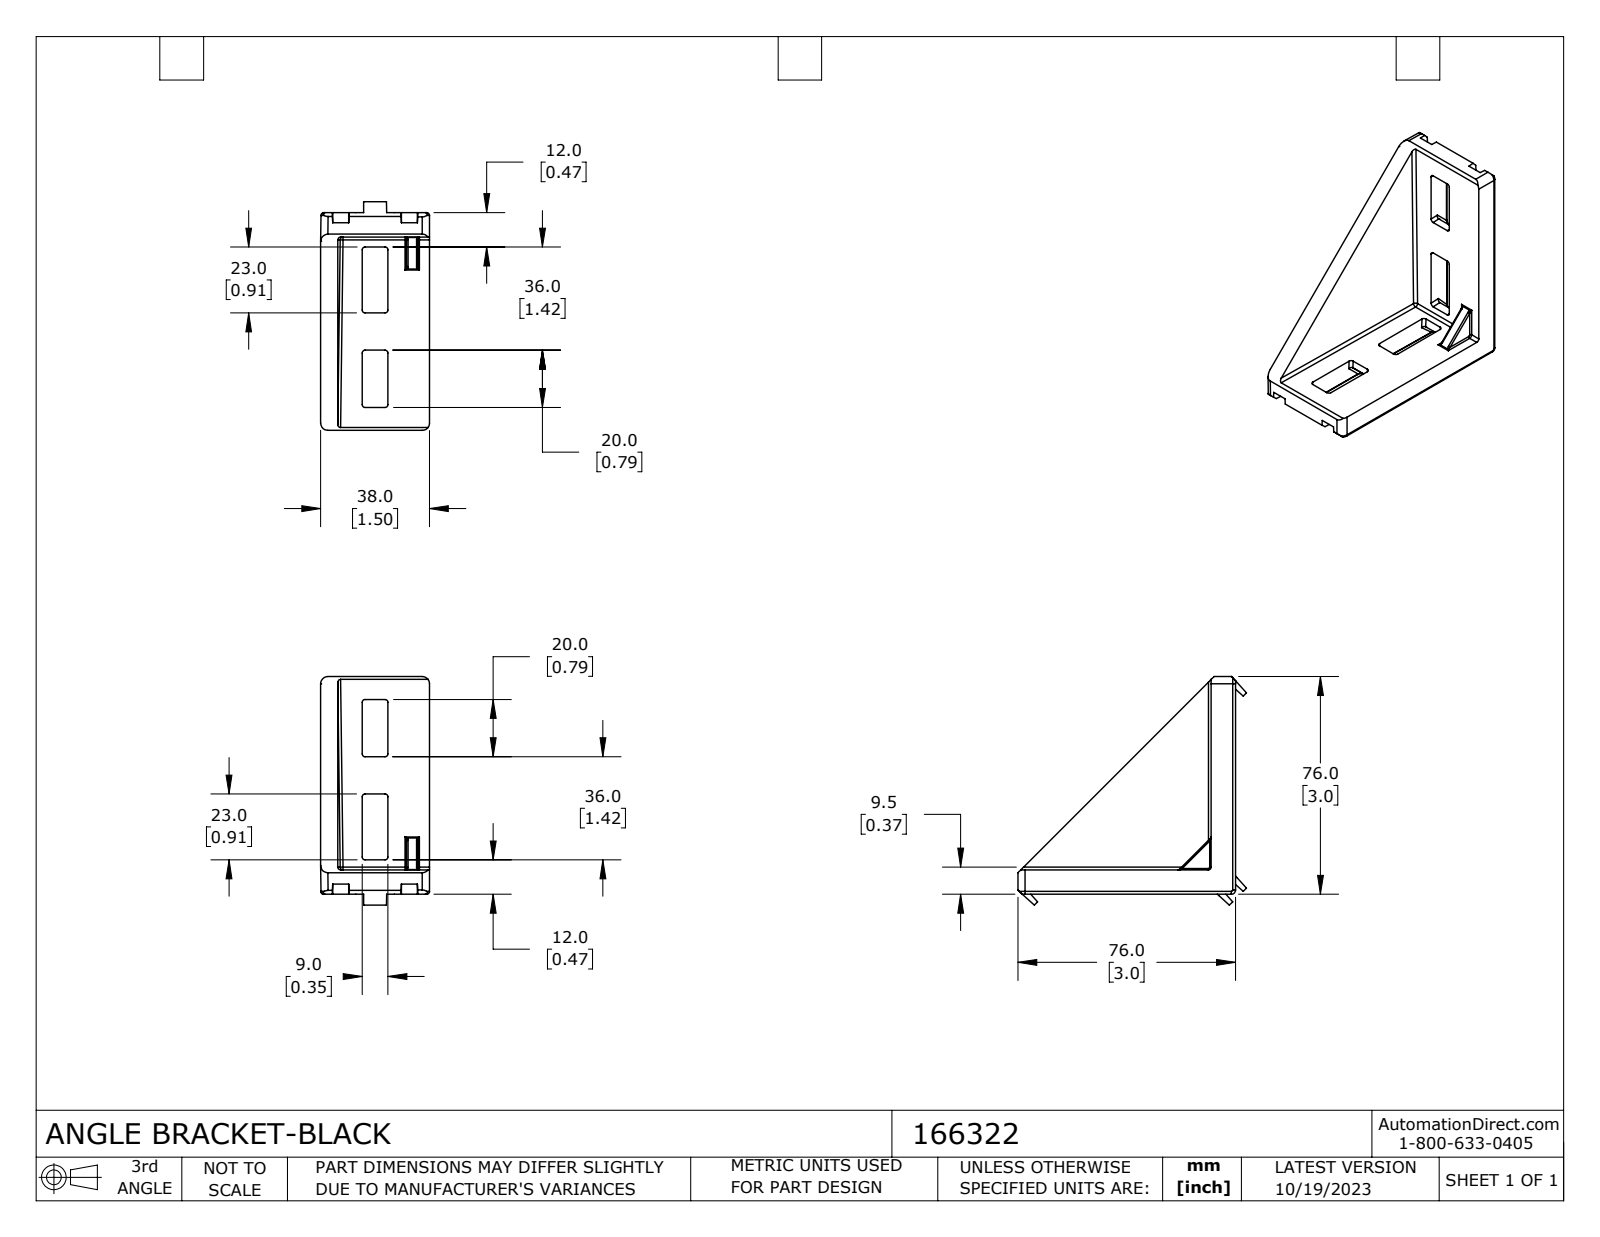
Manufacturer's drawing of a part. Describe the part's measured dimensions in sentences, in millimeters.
The part is named "166322". Its 3-D file was written by "SolidWorks 2023 (CONFIG_CONTROL_DESIGN)". It is 1 solid with 307 faces: 108 planar, 109 cylindrical and 90 other. Overall it measures 79.79 by 79.79 by 38 millimeters. Its volume is 44 633 cubic millimeters and its surface area 20 441 square millimeters. Partial cylindrical surfaces (rounded edges, fillets, slot ends): 51 of radius 1, 40 of radius 0.5, 4 of radius 2.5, 1 of radius 1.5. The main face-to-face distances are 6, 8.5, 4, 4.5, 23.97, 13.43, 10.54, 67.5, 72, 76.
